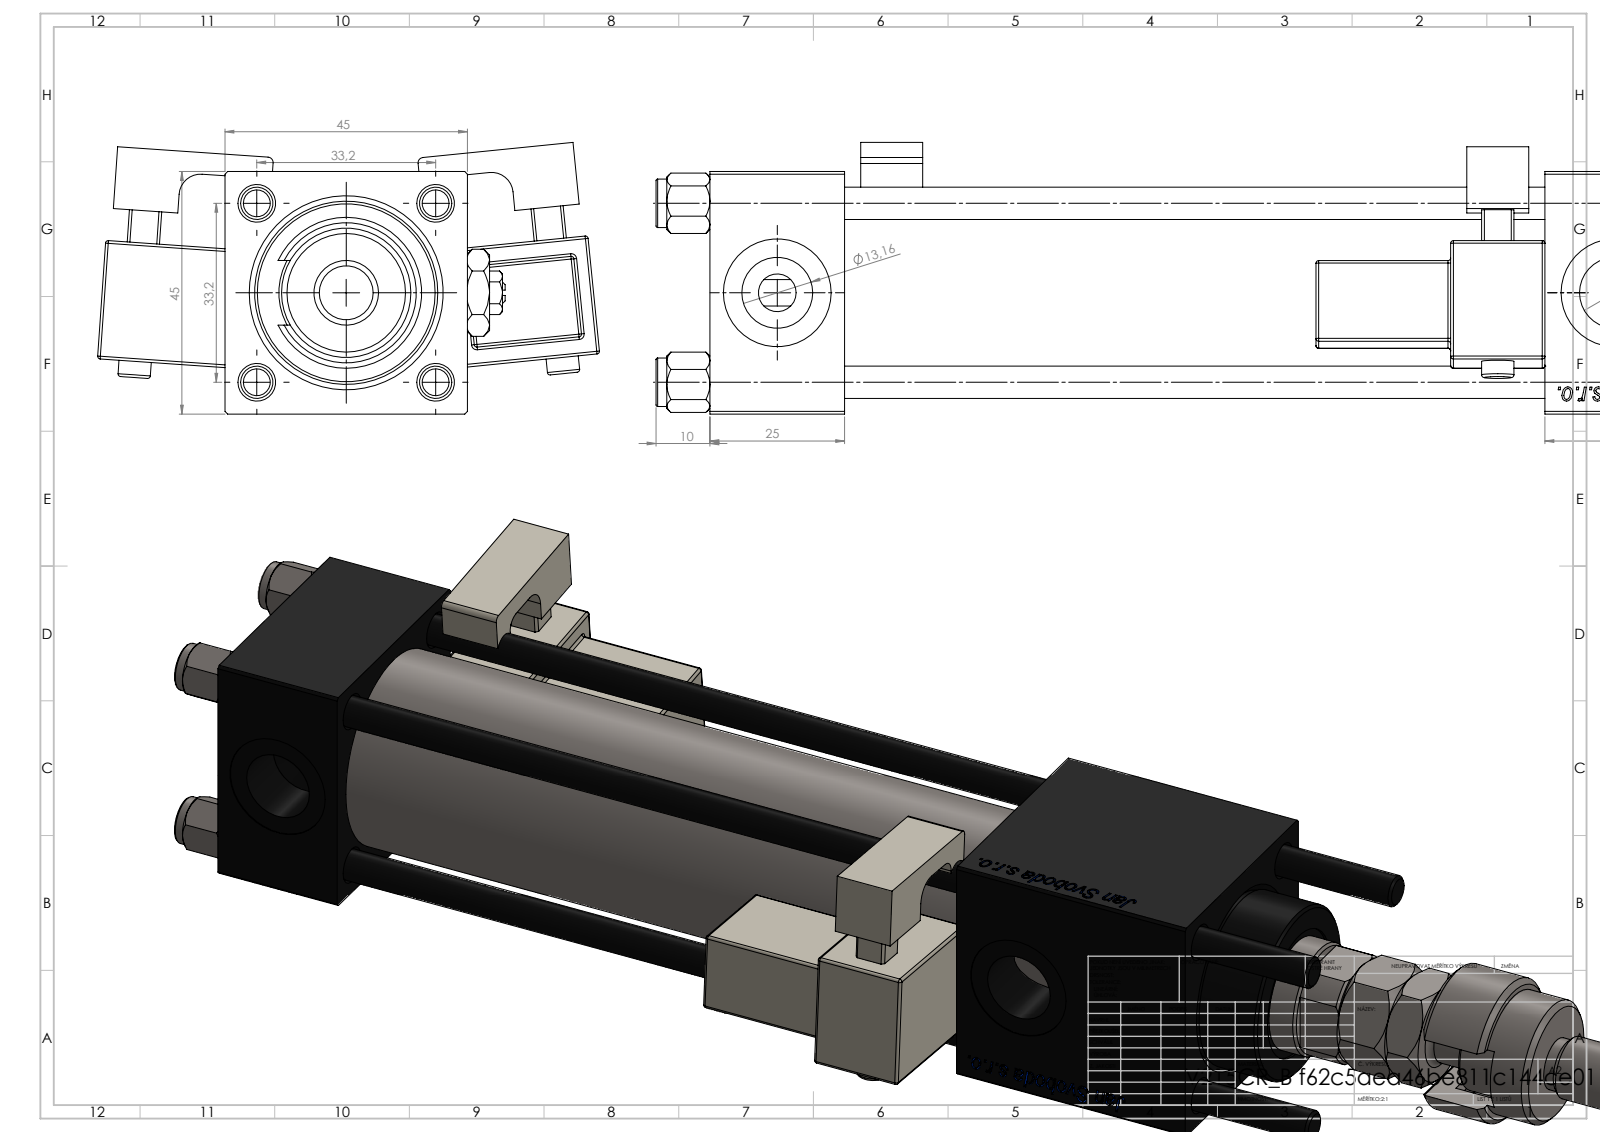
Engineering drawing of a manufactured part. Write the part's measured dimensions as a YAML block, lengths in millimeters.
part_name: "V215CR_B-1; FEMALE_PART_FOR_DFA; V215CR_B_TYCINKA; MFA (+5 more)"
step_written_by: "SolidWorks 2019 (CONFIG_CONTROL_DESIGN)"
units: millimeters
bodies: {solids: 17, faces: 1499, planar: 568, cylindrical: 161, other: 770}
overall_size: [299, 93.14, 50.4]
volume: 337166
surface_area: 126905
round_holes:
  - {diameter: 6, count: 4}
  - {diameter: 7, count: 2}
  - {diameter: 13.16, count: 2}
  - {diameter: 20, count: 2}
  - {diameter: 10.5, count: 1}
  - {diameter: 22, count: 1}
  - {diameter: 24, count: 1}
  - {diameter: 25, count: 1}
  - {diameter: 32, count: 1}
  - {diameter: 33, count: 1}
round_bosses_or_shafts:
  - {diameter: 9, count: 4}
  - {diameter: 6, count: 2}
  - {diameter: 38, count: 1}
  - {diameter: 34, count: 1}
  - {diameter: 28, count: 1}
  - {diameter: 18, count: 1}
  - {diameter: 12, count: 1}
  - {diameter: 11, count: 1}
partial_cylinders:
  - {radius: 0.5, count: 48}
  - {radius: 1, count: 2}
  - {radius: 2.5, count: 2}
  - {radius: 4, count: 2}
  - {radius: 9.75, count: 1}
  - {radius: 10.5, count: 1}
face_to_face_distances: [45, 25, 155, 130, 3, 203, 14.5, 15, 112.5, 17.5]
hole_center_spacings: [23.48, 33.2, 46.95, 155.5]
